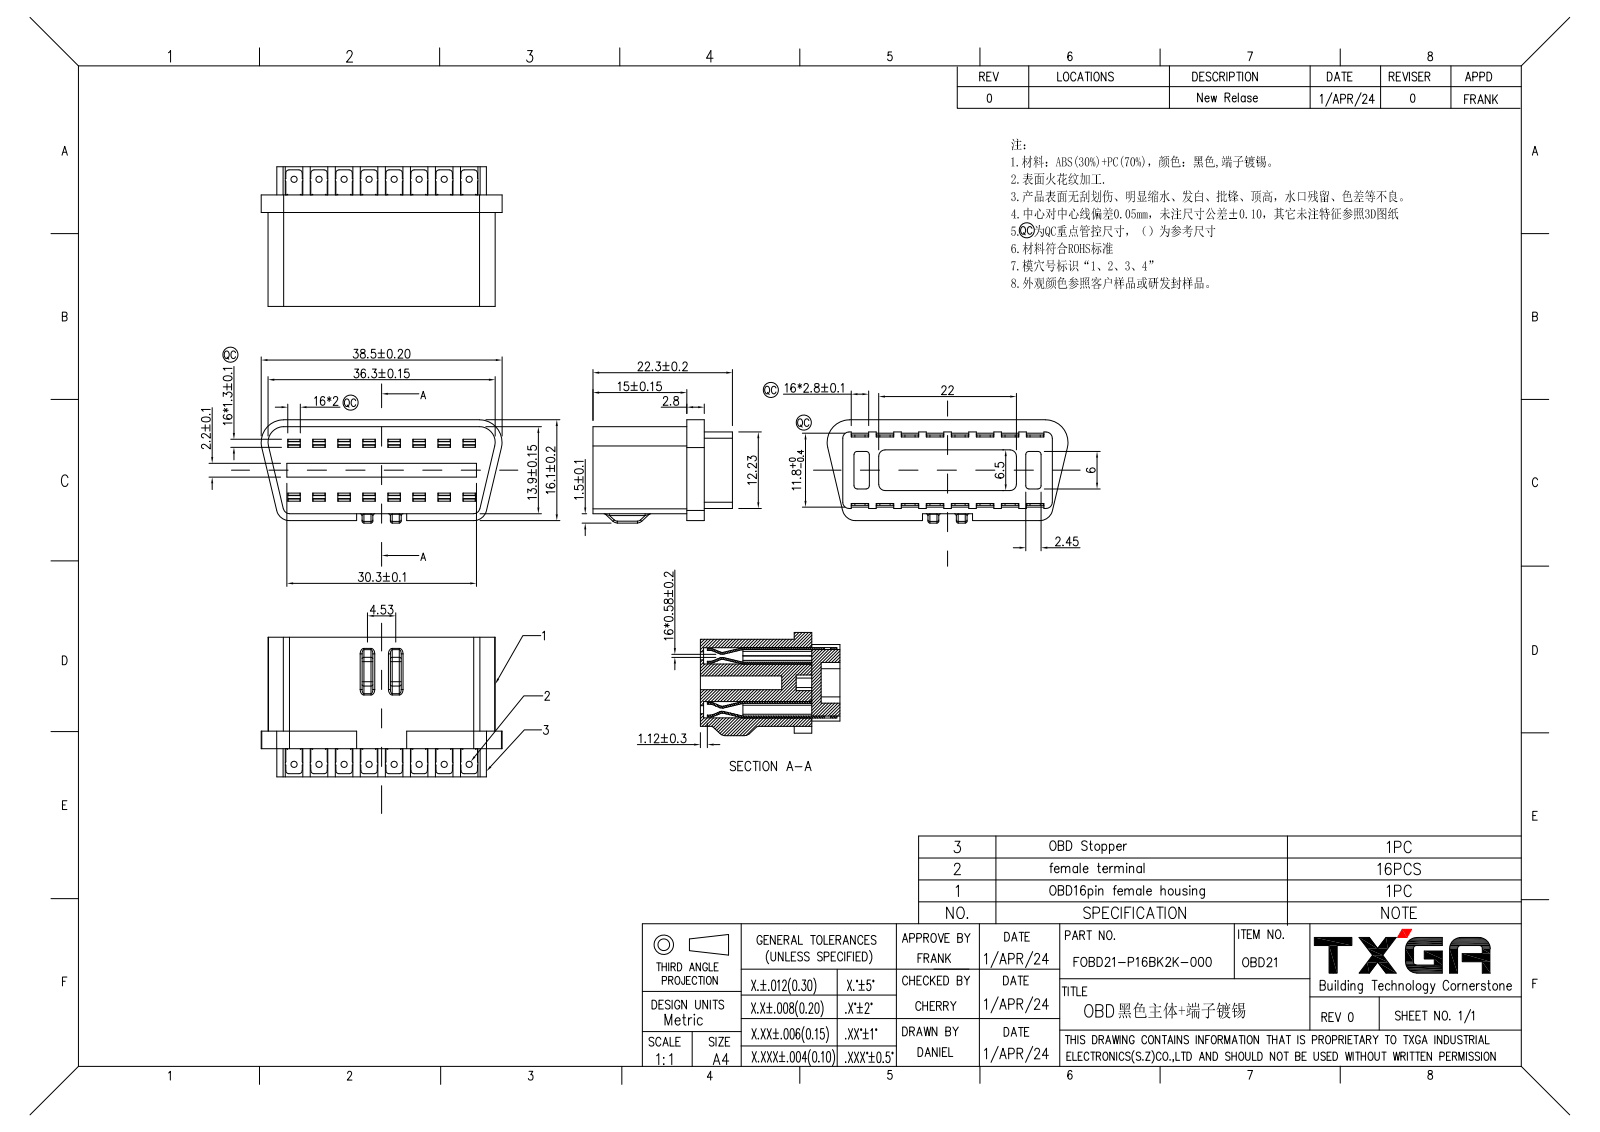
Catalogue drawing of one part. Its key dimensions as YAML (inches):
part_name: "PRT0002"
step_written_by: "PRO/ENGINEER BY PARAMETRIC TECHNOLOGY CORPORATION, 2010280 (CONFIG_CONTROL_DESIGN)"
units: inches
bodies: {solids: 0, faces: 3467, planar: 2351, cylindrical: 1096, other: 20}
overall_size: [1.516, 0.878, 0.65]
round_holes:
  - {diameter: 0.039, count: 8}
  - {diameter: 0.071, count: 1}
round_bosses_or_shafts:
  - {diameter: 0.072, count: 1}
partial_cylinders:
  - {radius: 0.012, count: 146}
  - {radius: 0.02, count: 52}
  - {radius: 0.039, count: 16}
  - {radius: 0.031, count: 8}
  - {radius: 0.051, count: 4}
  - {radius: 0.083, count: 2}
  - {radius: 0.098, count: 2}
  - {radius: 0.142, count: 2}
face_to_face_distances: [0.103, 0.339, 0.092, 0.327, 0.431, 0.104, 0.052, 0.012, 0.177, 0.064]
hole_center_spacings: [0.157, 0.315, 0.472, 0.63, 0.787, 0.945, 1.102]
